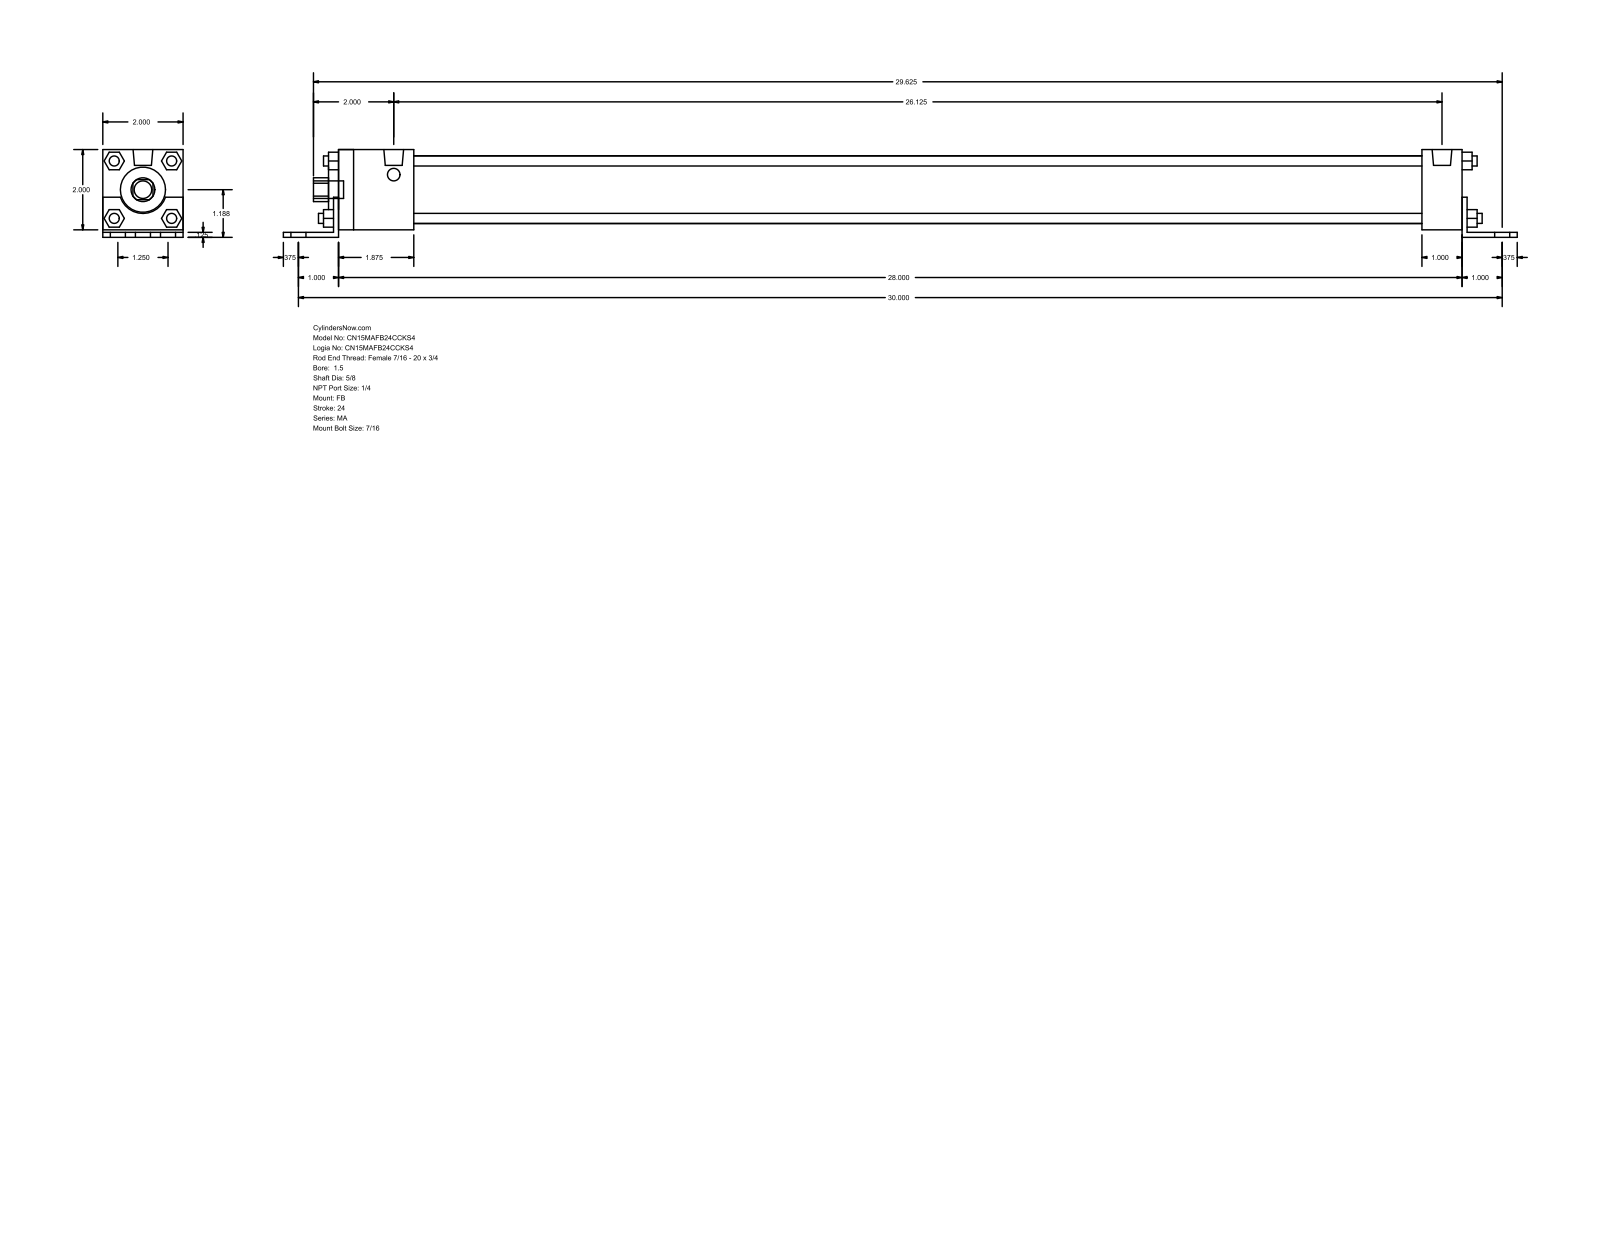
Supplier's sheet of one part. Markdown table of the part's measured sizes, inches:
| quantity | value |
| --- | --- |
| part name | MA_FB__0150_0.625 |
| STEP written by | GSSL Pune (CONFIG_CONTROL_DESIGN) |
| units | inches |
| bodies | 0 solids, 140 faces (105 planar, 35 cylindrical, 0 other) |
| overall size | 30.75 × 2.187 × 2 |
| round holes (diameter × count) | 0.625 × 1, 1.125 × 1, 1.69 × 1 |
| round bosses / shafts (diameter × count) | 0.437 × 7, 0.313 × 4, 0.25 × 4, 0.492 × 2 |
| partial cylindrical surfaces (radius × count) | 0.297 × 1, 0.593 × 1 |
| main face-to-face distances | 2, 0.125, 0.187, 2.187, 0.063, 2.063, 28.25, 0.25, 28, 1.125 |
